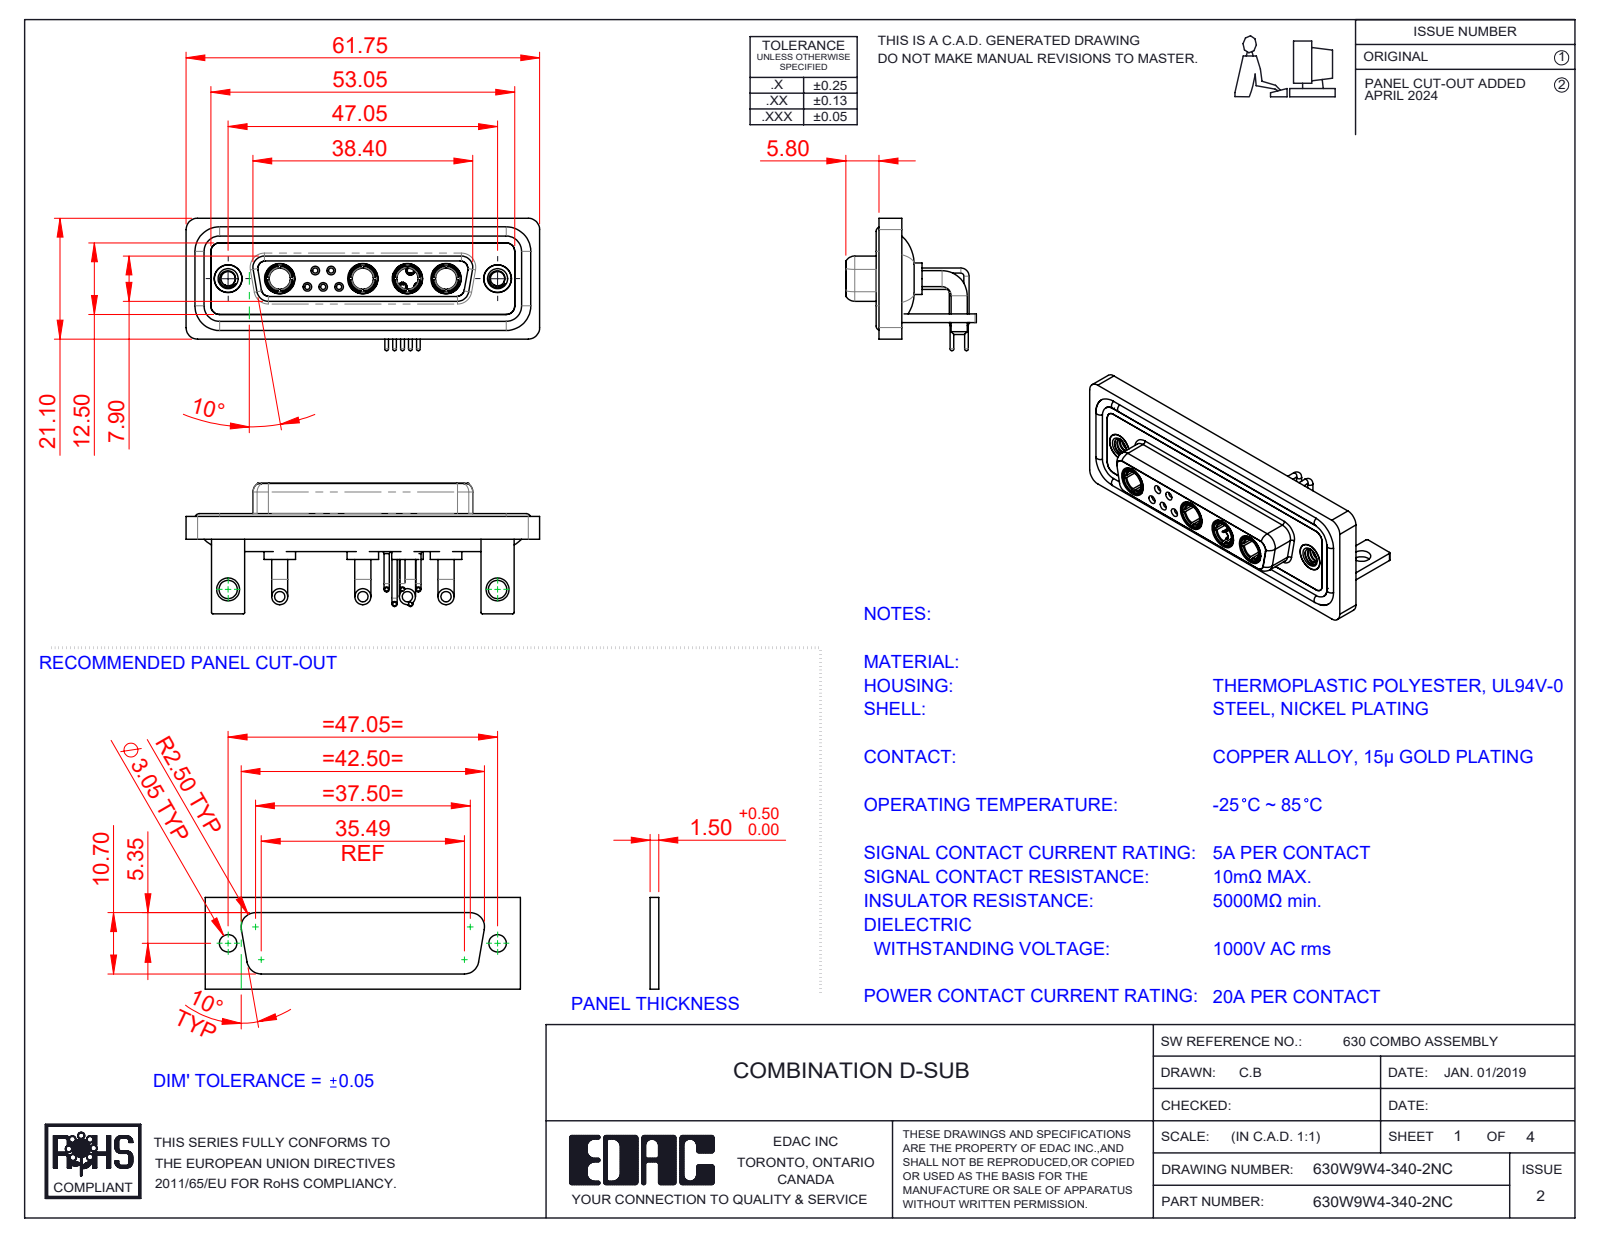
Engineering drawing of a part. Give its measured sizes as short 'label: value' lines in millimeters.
name: 630Combo Shell Rear_25 Contacts; 630Combo Waterproof Housing_25 Contacts; 630Combo Threaded Rivet_A; 630Combo Contact Row 1_50 Contacts (+6 more)
written by: SolidWorks 2023 (CONFIG_CONTROL_DESIGN)
unit: mm
bodies: 22 solids, 1005 faces (316 planar, 425 cylindrical, 264 other)
size: 61.75 × 23.12 × 22.8
volume: 8 811 mm³; area: 14 785 mm²
holes: 6× ⌀4.85, 5× ⌀0.9, 5× ⌀1.1, 5× ⌀1.5, 5× ⌀2, 4× ⌀3.7, 4× ⌀5.3, 3× ⌀1.6, 2× ⌀1.7, 2× ⌀2.5, 2× ⌀3.2, 2× ⌀4
bosses: 10× ⌀0.9, 9× ⌀1.6, 8× ⌀2.8, 5× ⌀2, 5× ⌀1.5, 5× ⌀0.65, 4× ⌀5.5, 4× ⌀5.2
rounds: 19× R2, 18× R1.5, 16× R0.25, 8× R1.35, 8× R1.6, 5× R0.5, 4× R0.6, 4× R0.65
face distances: 0.4, 1.8, 2.9, 3.7, 1.5, 4.1, 1.1, 1.4, 1.6, 2.5
hole spacings: 3.16, 2.77, 5.04, 13.85, 11.08, 12.79, 15.5, 5.54
